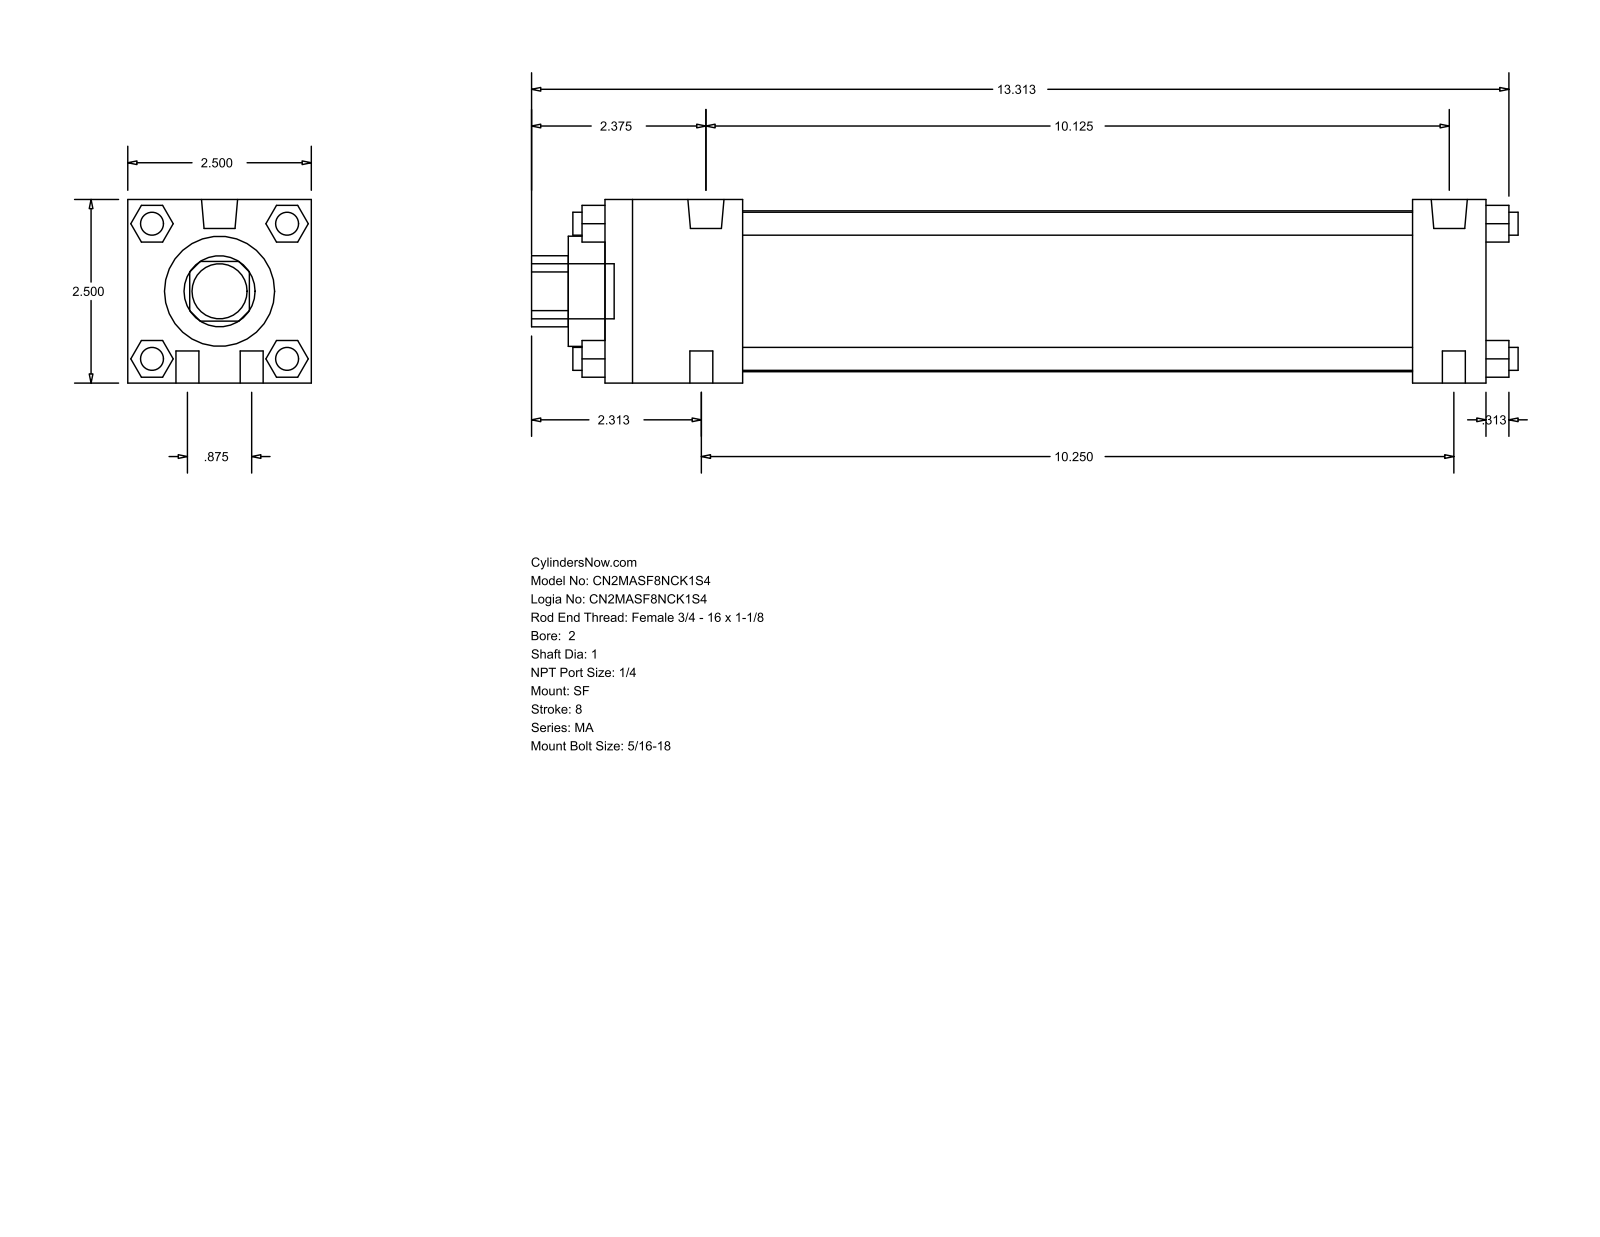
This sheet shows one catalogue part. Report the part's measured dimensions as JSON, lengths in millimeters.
{"part_name": "MA_SF__0200_1", "step_written_by": "GSSL Pune (CONFIG_CONTROL_DESIGN)", "units": "millimeters", "bodies": {"solids": 0, "faces": 124, "planar": 94, "cylindrical": 30, "other": 0}, "overall_size": [341.31, 63.5, 63.5], "round_holes": [[25.4, 1], [38.1, 1], [55.63, 1]], "round_bosses_or_shafts": [[7.94, 10], [12.49, 2], [19.05, 1]], "partial_cylinders_radius": [[12.29, 1]], "face_to_face_distances": [63.5, 304.8, 12.7, 25.4, 279.4, 47.63, 231.77, 257.17, 23.37, 40.47]}
